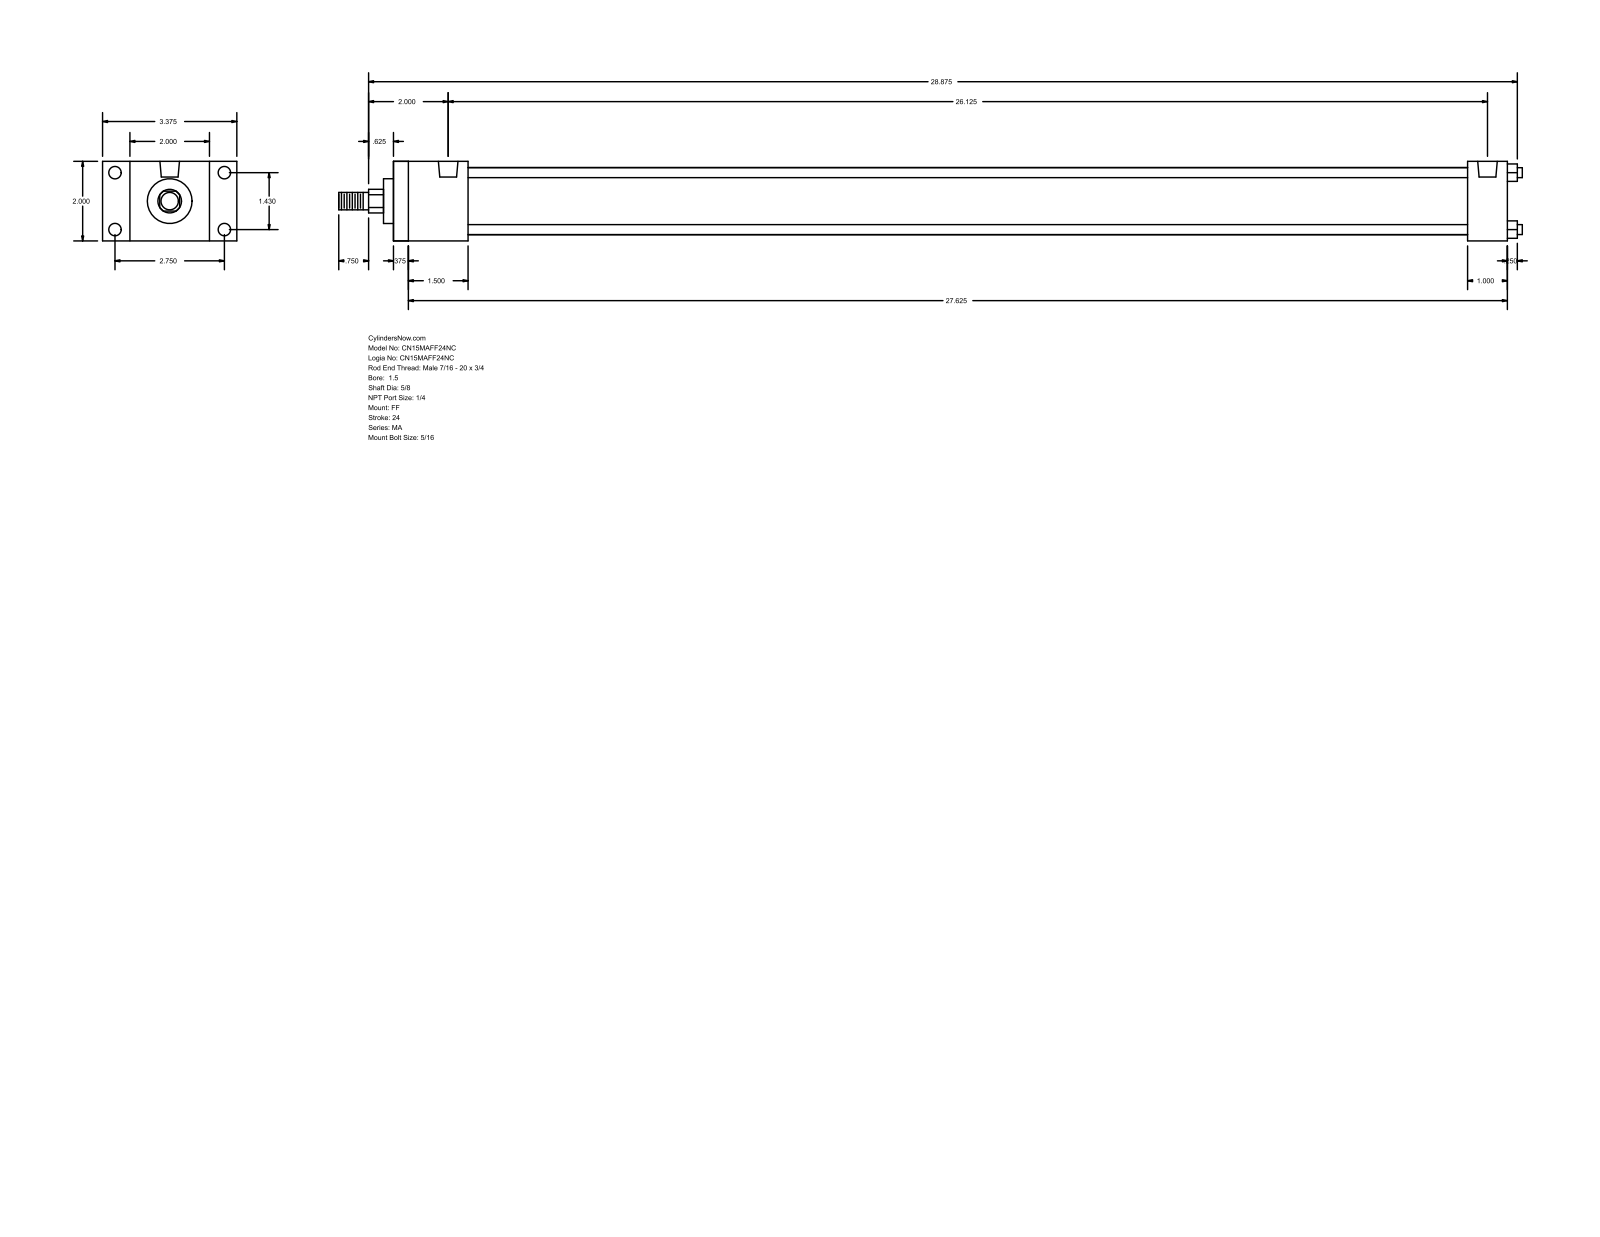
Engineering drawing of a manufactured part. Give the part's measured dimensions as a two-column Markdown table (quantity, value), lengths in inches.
| quantity | value |
| --- | --- |
| part name | MA_FF__0150_0.625 |
| STEP written by | GSSL Pune (CONFIG_CONTROL_DESIGN) |
| units | inches |
| bodies | 0 solids, 92 faces (64 planar, 28 cylindrical, 0 other) |
| overall size | 29.75 × 3.375 × 2 |
| round holes (diameter × count) | 0.313 × 8, 0.492 × 2 |
| round bosses / shafts (diameter × count) | 0.25 × 4, 1.69 × 1, 1.125 × 1, 0.625 × 1, 0.437 × 1 |
| partial cylindrical surfaces (radius × count) | 0.297 × 1 |
| main face-to-face distances | 2, 28, 0.375, 27.625, 1.875, 27, 1.5, 26.625, 25.125, 26.125 |
| hole center spacings | 1.43, 2.75, 3.099, 26.125 |
